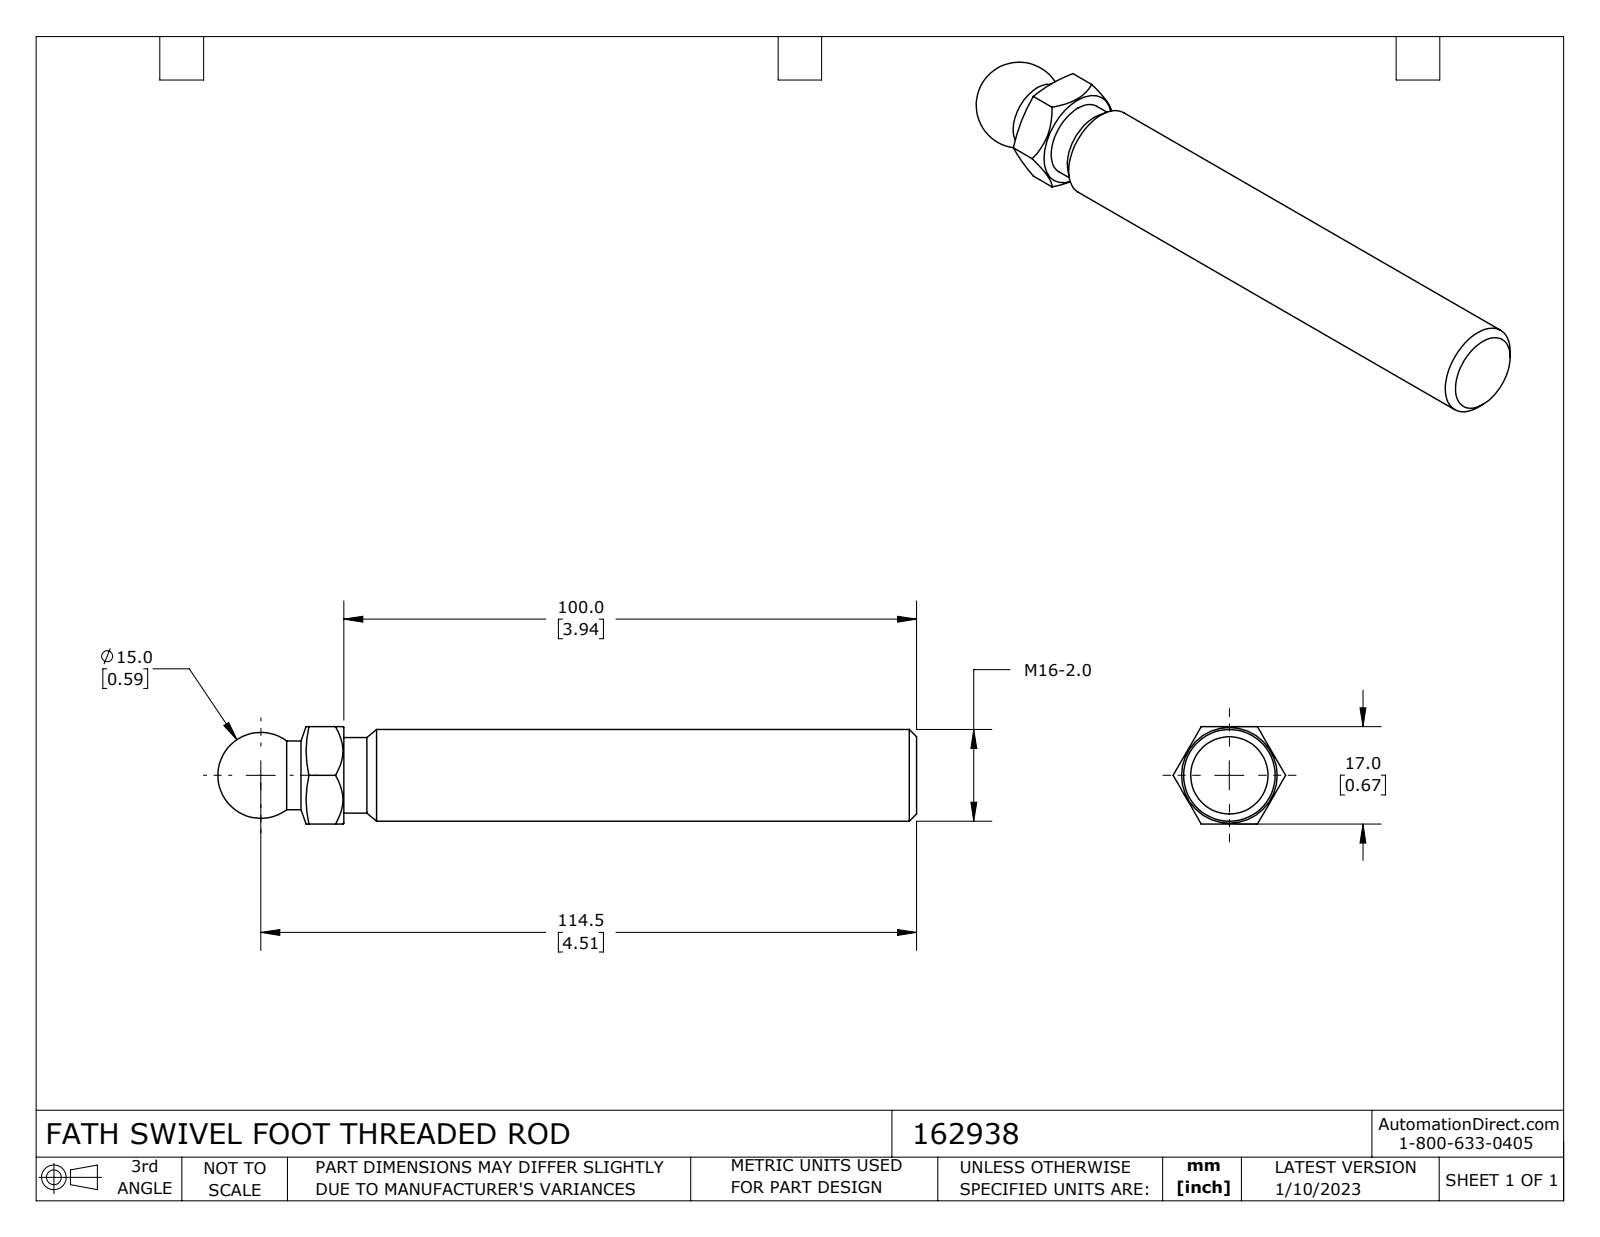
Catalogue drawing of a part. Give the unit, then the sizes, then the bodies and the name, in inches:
Units: inches
Overall size (bounding box): 4.791 × 0.773 × 0.669
Round bosses / shafts (diameter × count): ⌀0.63 ×1, ⌀0.52 ×1, ⌀0.472 ×1
Main face-to-face distances: 0.669, 3.937
Volume: 1.428 in³ · Surface area: 9.988 in²
Bodies: 1 solid, 24 faces (8 planar, 6 cylindrical, 10 other)
Part name (STEP PRODUCT): 162938
STEP written by: SolidWorks 2021 (CONFIG_CONTROL_DESIGN)
